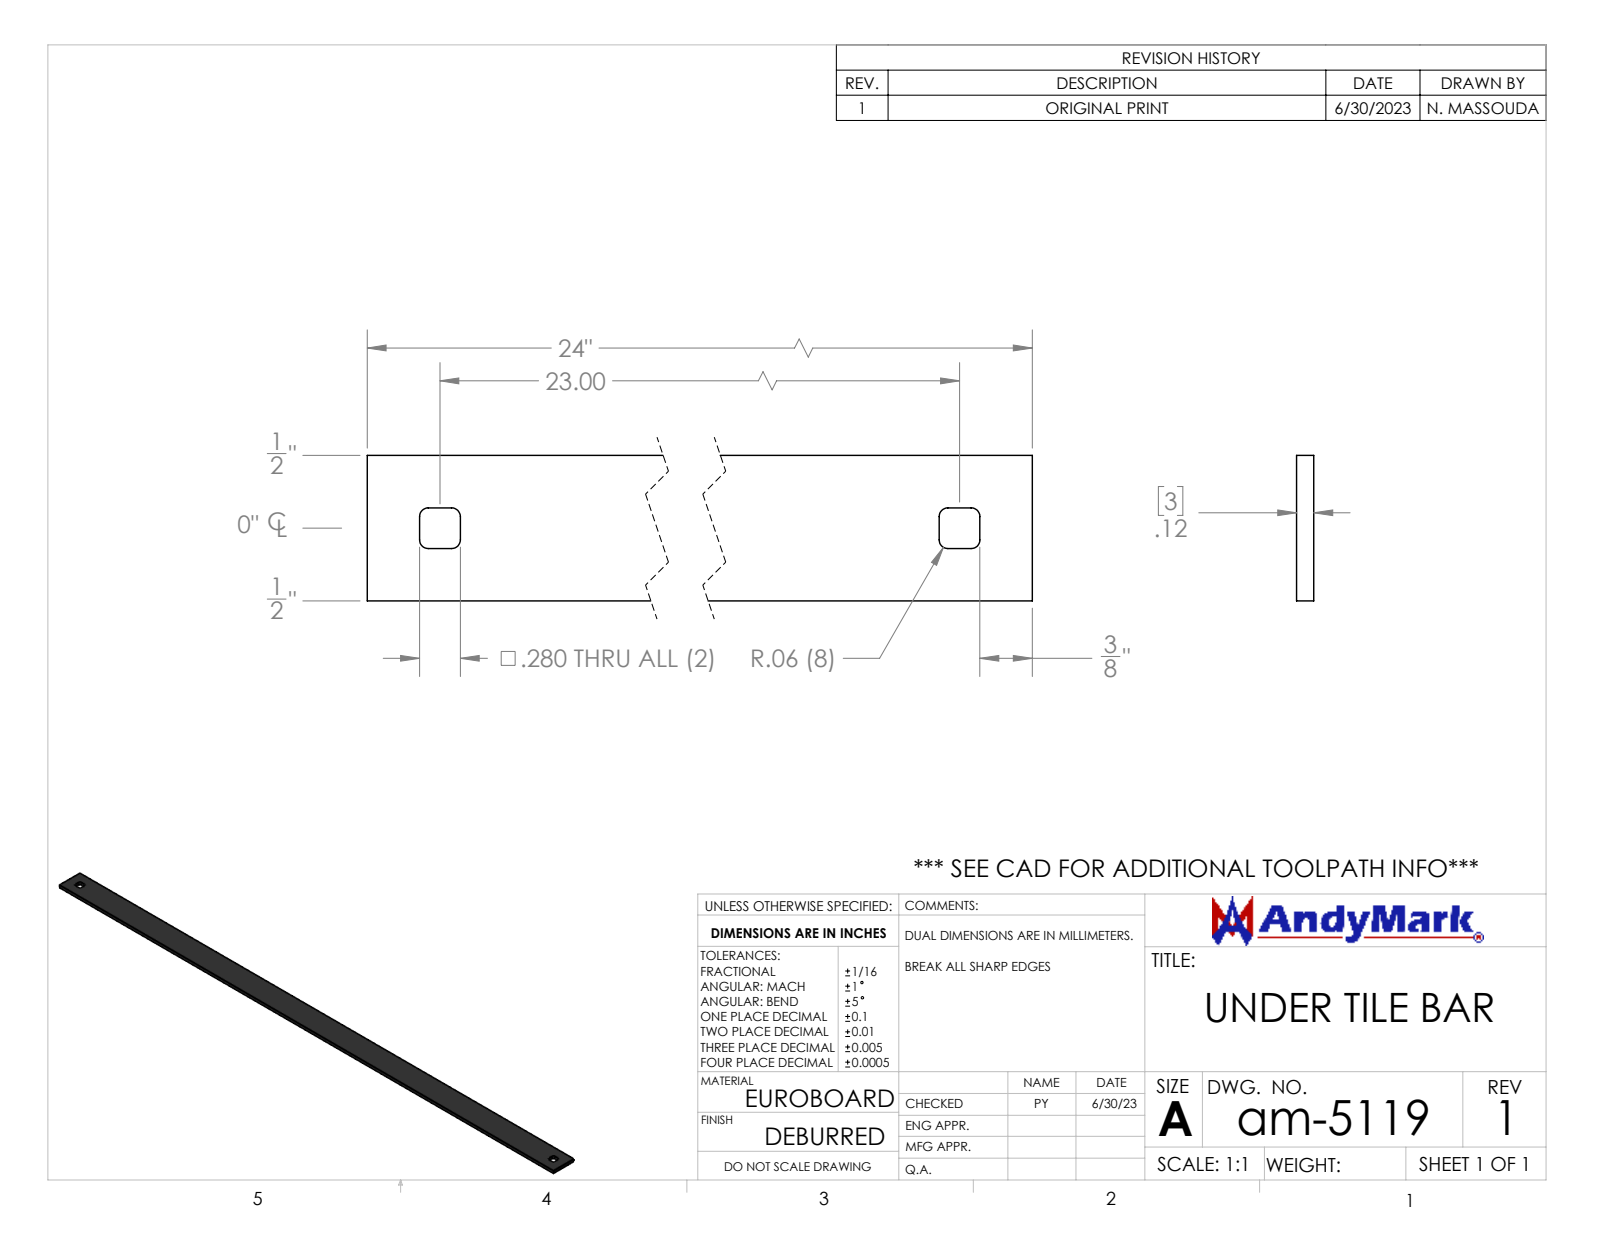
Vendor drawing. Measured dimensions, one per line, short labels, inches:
name: am-5119 Under Tile Bar
written by: SolidWorks 2022 (CONFIG_CONTROL_DESIGN)
unit: in
bodies: 1 solid, 22 faces (14 planar, 8 cylindrical, 0 other)
size: 24 × 1 × 0.118
volume: 2.814 in³; area: 53.84 in²
rounds: 8× R0.06
face distances: 0.118, 1, 24, 0.36, 0.64, 0.28, 23.64, 23.36, 23, 23.28
